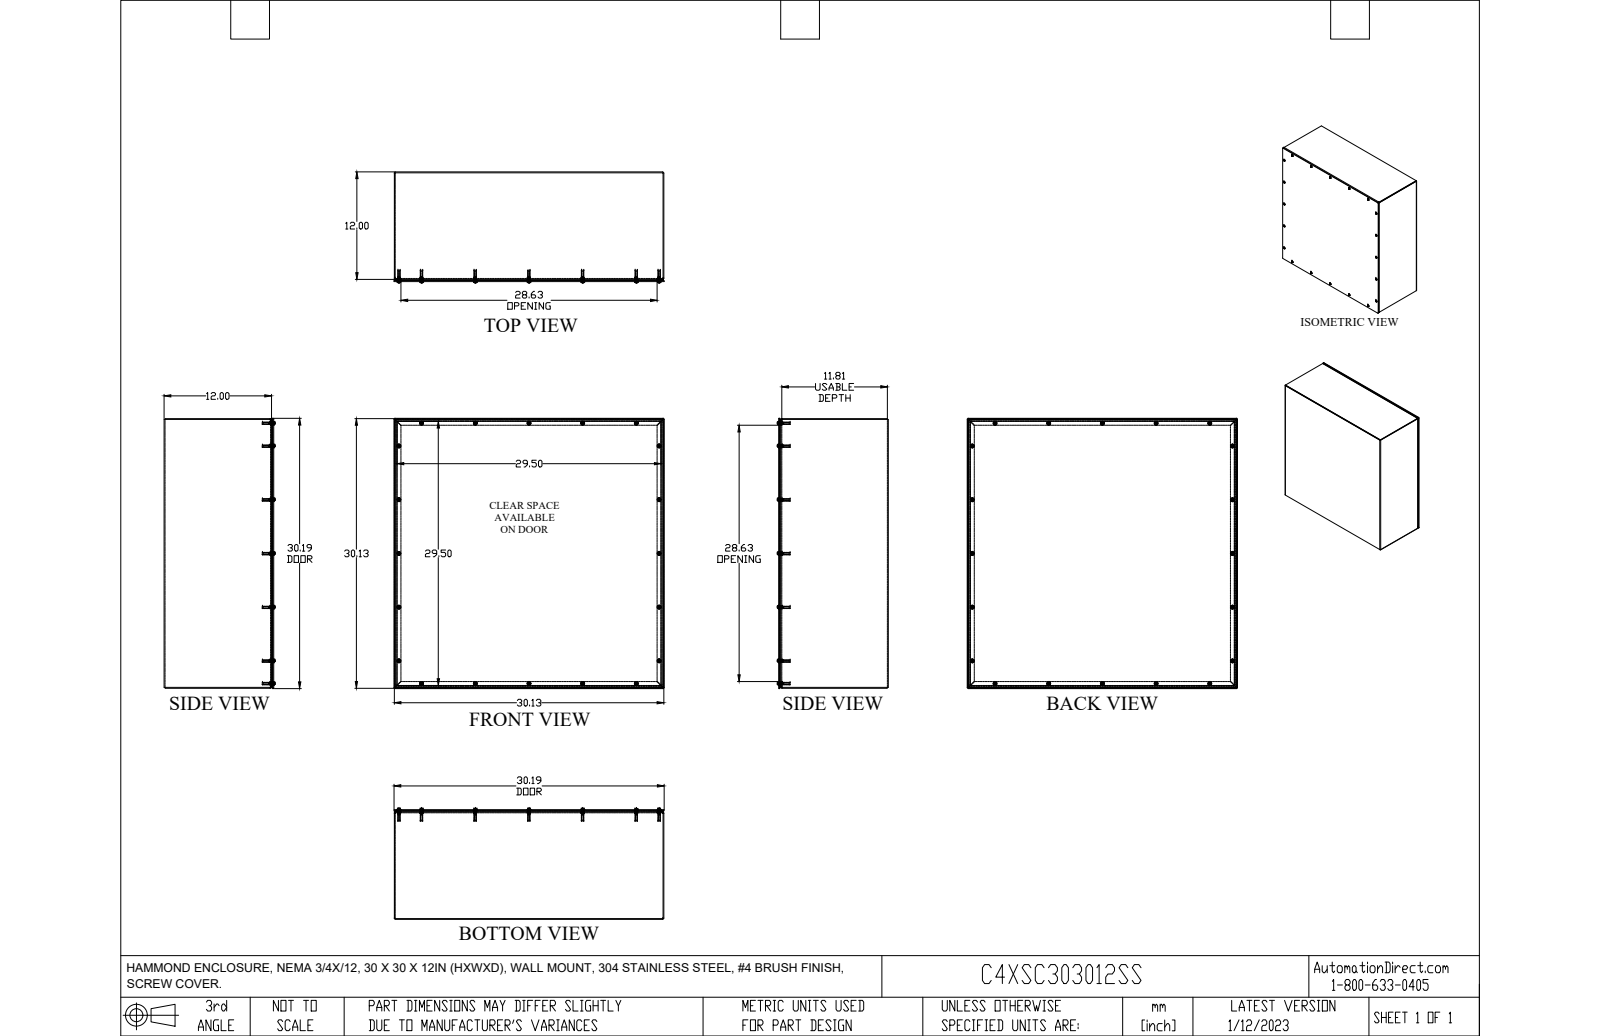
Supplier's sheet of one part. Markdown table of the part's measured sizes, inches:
| quantity | value |
| --- | --- |
| part name | C3SC303012GY |
| STEP written by | SolidWorks 2021 (AUTOMOTIVE_DESIGN) |
| units | inches |
| bodies | 64 solids, 1858 faces (1162 planar, 328 cylindrical, 368 other) |
| overall size | 30.188 × 30.188 × 12.4 |
| volume | 345.6 in³ |
| surface area | 6 798 in² |
| round holes (diameter × count) | 0.159 × 20, 0.16 × 20, 0.25 × 20 |
| round bosses / shafts (diameter × count) | 0.44 × 20, 0.39 × 20, 0.275 × 20, 0.24 × 20, 0.19 × 20, 0.148 × 20 |
| partial cylindrical surfaces (radius × count) | 0.16 × 20, 0.125 × 8, 0.048 × 6, 0.143 × 6, 0.126 × 4, 0.374 × 4 |
| main face-to-face distances | 0.095, 30.03, 0.095, 12.155, 12.25, 0.125, 12.03, 12.125, 29.935, 30.125 |
| hole center spacings | 6, 29.687, 12, 31.454, 29.075, 8.906, 14.757, 16.859 |
